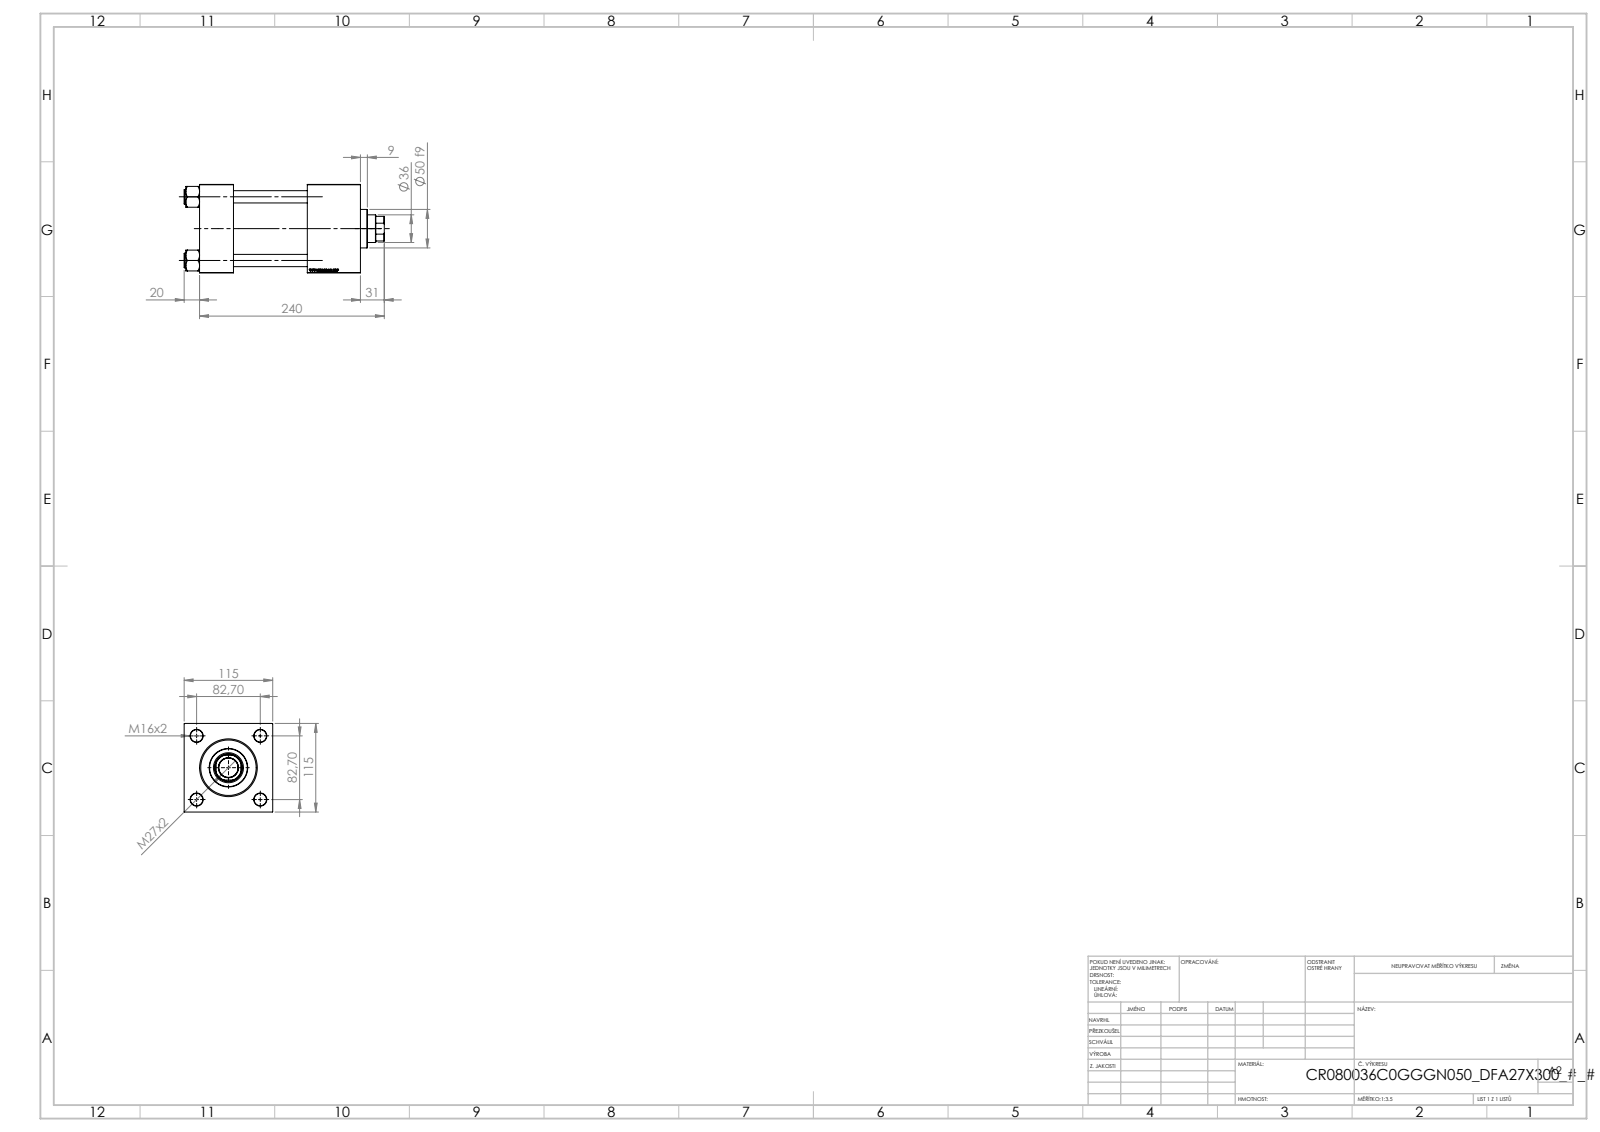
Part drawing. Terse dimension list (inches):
name: NUT_M5_C; V215_VC_A; V215CR_VCP_C; FEMALE_PART_FOR_DFA (+2 more)
written by: SolidWorks 2019 (CONFIG_CONTROL_DESIGN)
unit: in
bodies: 12 solids, 1230 faces (586 planar, 96 cylindrical, 548 other)
size: 10.236 × 4.528 × 4.528
volume: 116.8 in³; area: 474 in²
holes: 4× ⌀0.63, 2× ⌀0.276, 2× ⌀1.041, 2× ⌀1.378, 1× ⌀1.004, 1× ⌀1.535, 1× ⌀2.402, 1× ⌀2.835, 1× ⌀3.15
bosses: 4× ⌀0.748, 1× ⌀3.386, 1× ⌀1.969, 1× ⌀1.732, 1× ⌀1.417, 1× ⌀1.063, 1× ⌀0.984
rounds: 1× R0.374, 1× R0.591, 1× R0.689
face distances: 4.528, 1.732, 8.228, 6.496, 2.717, 5.512, 3.78, 3.543, 1.969, 7.098
hole spacings: 2.302, 3.256, 4.605, 5.551
